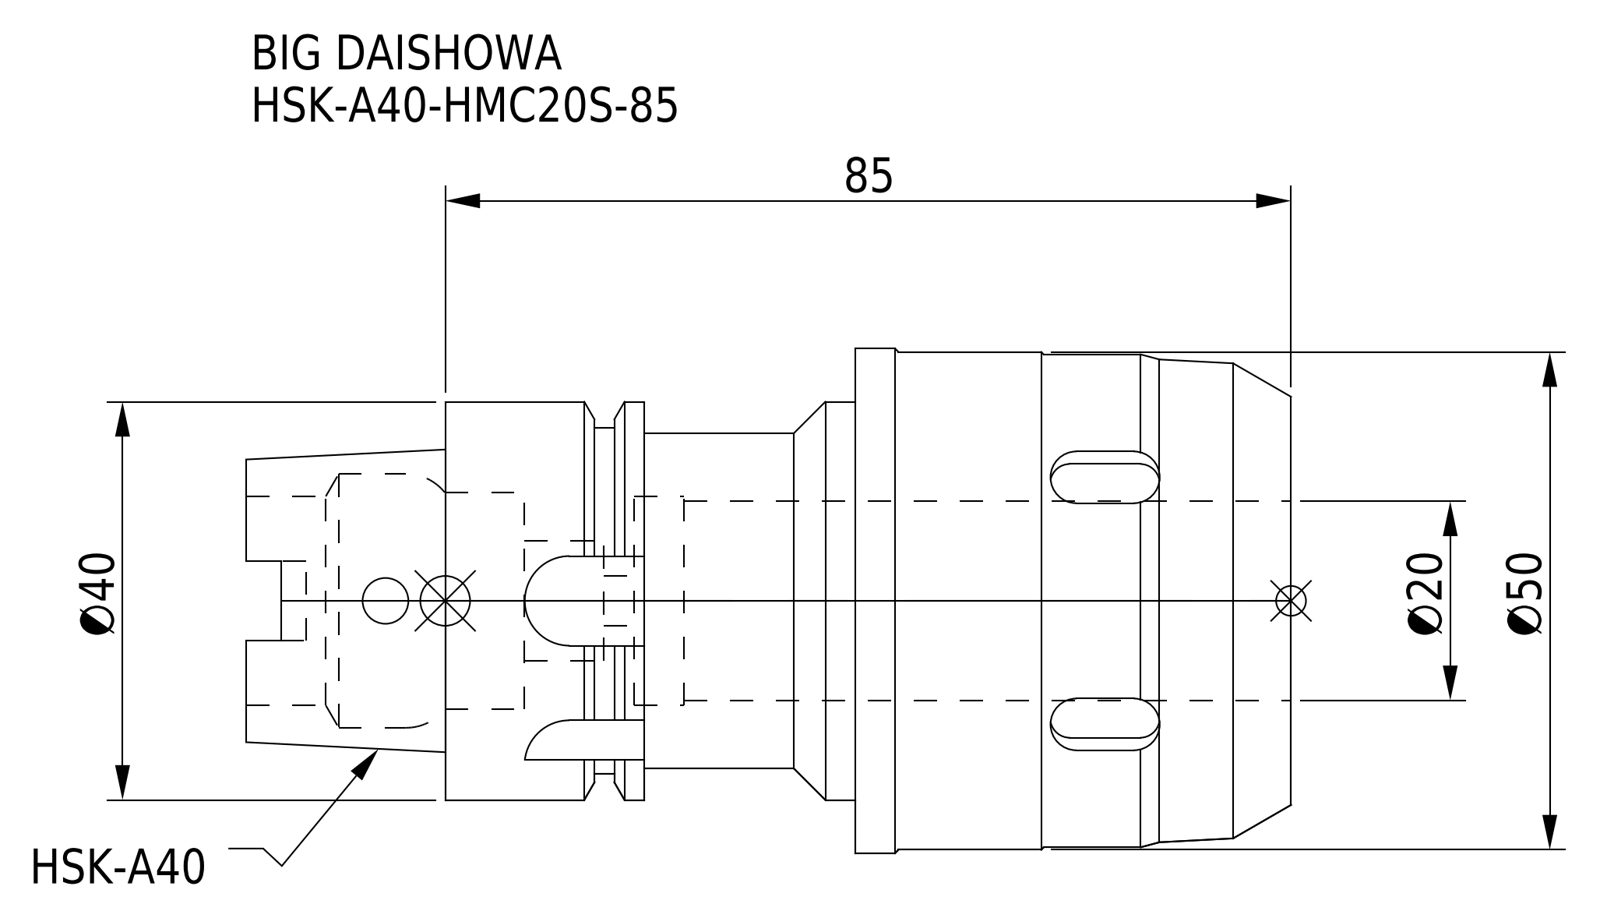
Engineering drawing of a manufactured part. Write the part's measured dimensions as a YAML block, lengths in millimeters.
part_name: "HSK-A40-HMC20S-85"
step_written_by: "CREO PARAMETRIC BY PTC INC, 2016380 (AUTOMOTIVE_DESIGN)"
units: millimeters
bodies: {solids: 1, faces: 143, planar: 57, cylindrical: 58, other: 28}
overall_size: [105, 50.7, 50.7]
volume: 105419
surface_area: 24696
round_holes:
  - {diameter: 4.6, count: 1}
  - {diameter: 5, count: 1}
  - {diameter: 12, count: 1}
  - {diameter: 20, count: 1}
  - {diameter: 21, count: 1}
  - {diameter: 21.8, count: 1}
  - {diameter: 25.5, count: 1}
round_bosses_or_shafts:
  - {diameter: 50.7, count: 1}
  - {diameter: 50, count: 1}
  - {diameter: 49.5, count: 1}
  - {diameter: 40, count: 1}
  - {diameter: 34.8, count: 1}
  - {diameter: 33.6, count: 1}
partial_cylinders:
  - {radius: 3, count: 6}
  - {radius: 1.88, count: 4}
  - {radius: 4.5, count: 4}
face_to_face_distances: [43.8, 20, 85, 41.2, 66, 22.2, 19, 1, 65, 21.2]
